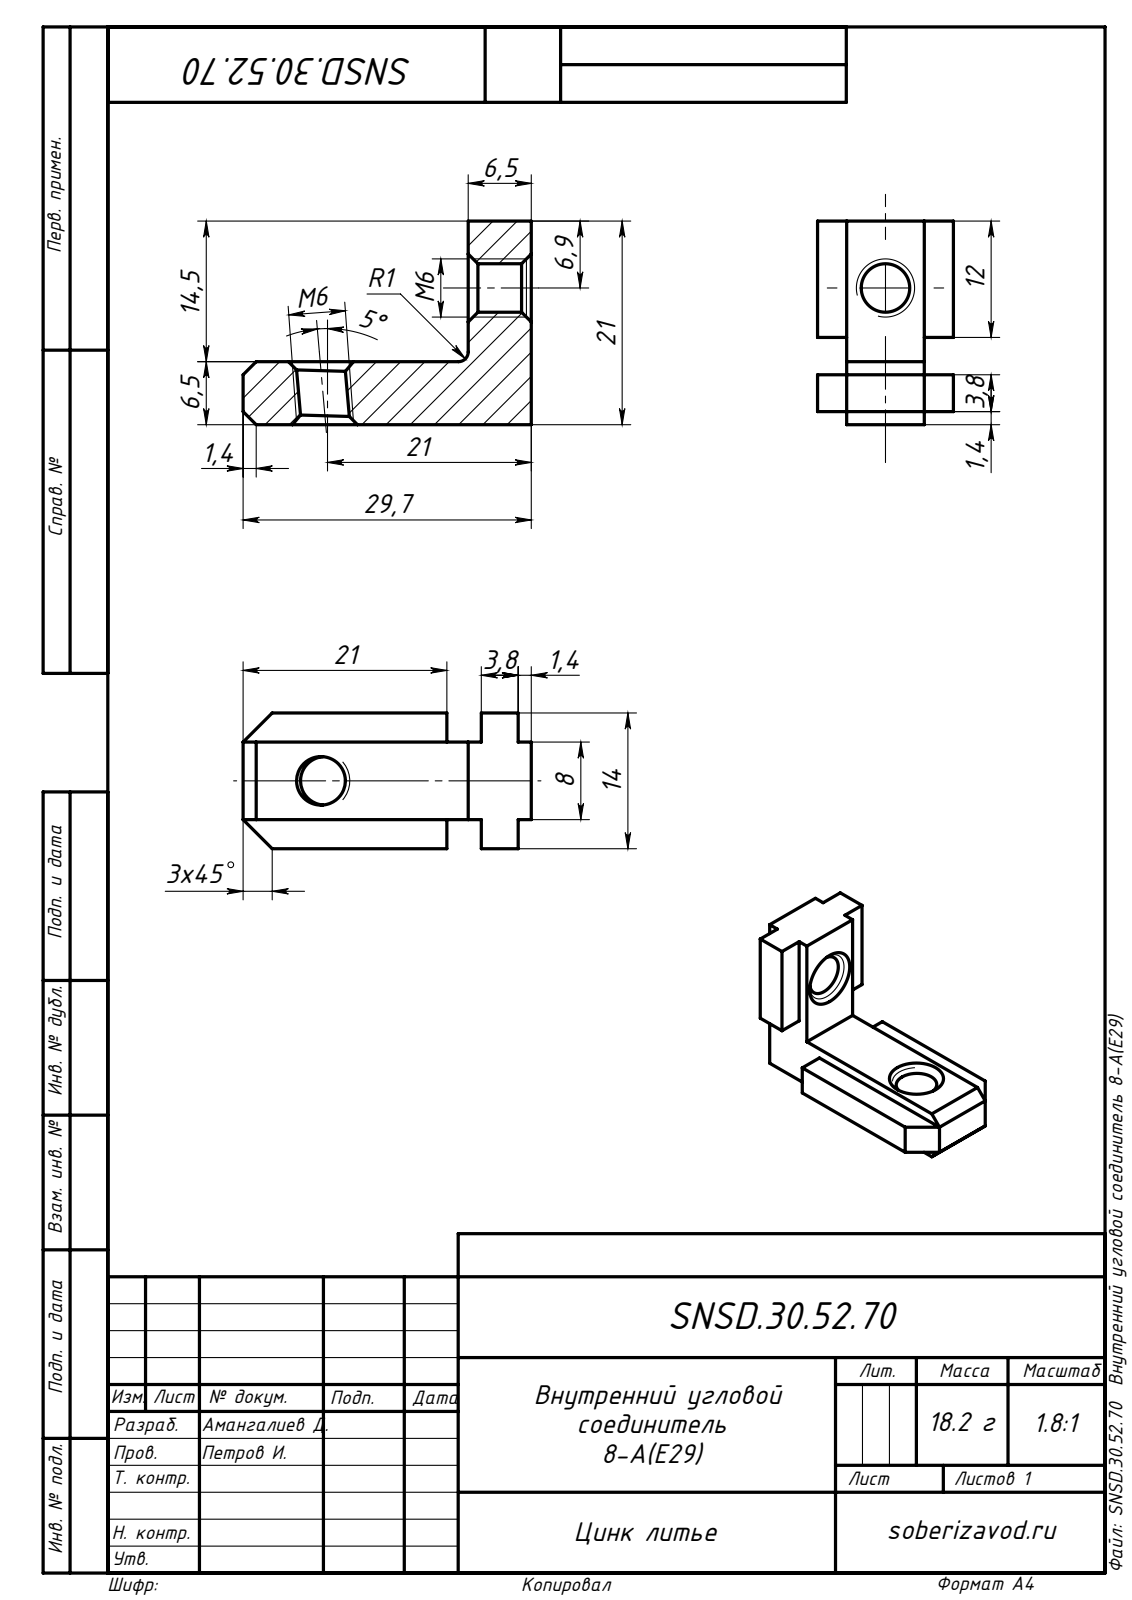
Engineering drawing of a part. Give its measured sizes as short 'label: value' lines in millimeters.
written by: SolidWorks 2014 (AUTOMOTIVE_DESIGN)
unit: mm
bodies: 1 solid, 41 faces (28 planar, 5 cylindrical, 8 other)
size: 29.7 × 21 × 14
volume: 2 717 mm³; area: 1 918 mm²
holes: 2× ⌀5
rounds: 1× R1
face distances: 1.35, 5.15, 3, 11, 6.5, 3.8, 8, 14, 21, 19.65
